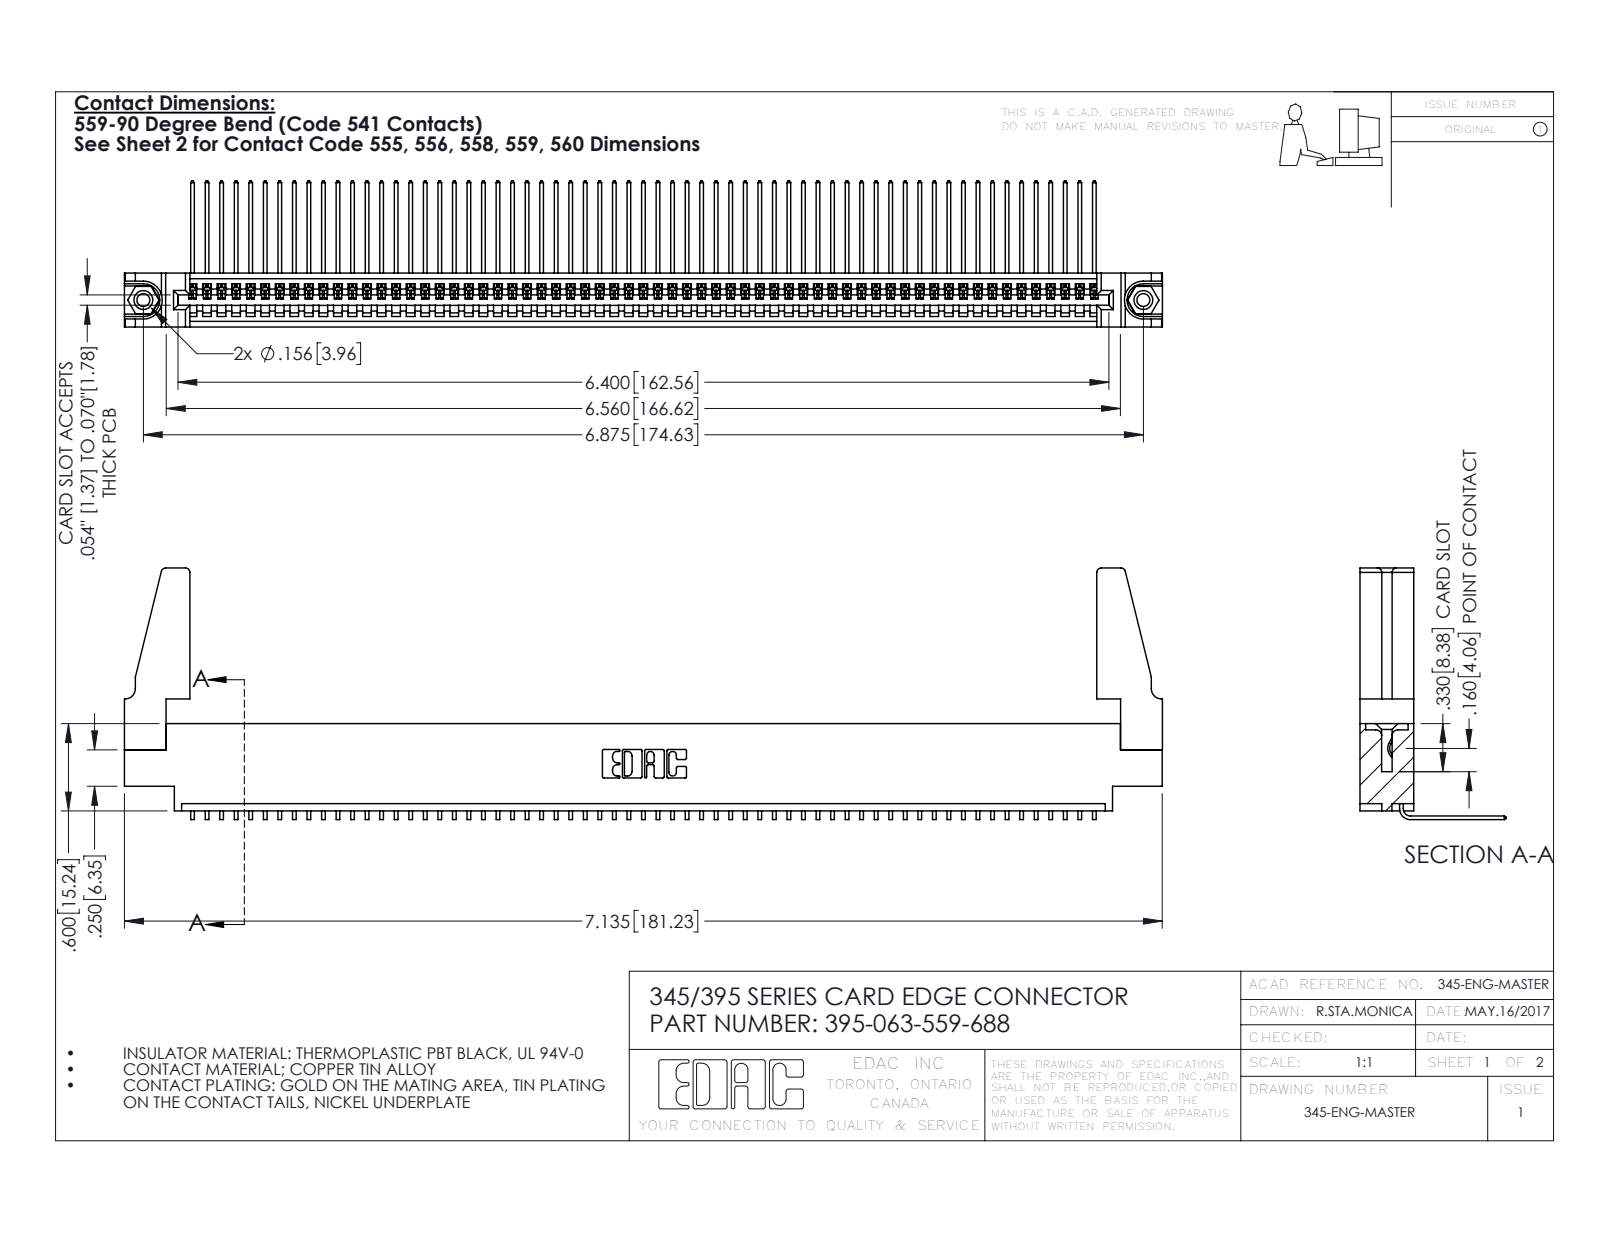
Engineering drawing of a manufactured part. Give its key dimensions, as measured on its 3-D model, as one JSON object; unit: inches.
{"part_name": "345-220-078_345-220-088; 345 Part_0.170 Offset - 0.156 Dia-TH; 345-250-001_345-250-001-102; 345-292-001_558 559 Tail - 1 (+1 more)", "step_written_by": "SolidWorks 2016 (CONFIG_CONTROL_DESIGN)", "units": "inches", "bodies": {"solids": 68, "faces": 4034, "planar": 2802, "cylindrical": 1216, "other": 16}, "overall_size": [7.136, 1.729, 1.005], "volume_in3": 1.265, "surface_area_in2": 43.42, "round_holes": [[0.089, 2], [0.125, 2], [0.156, 2], [0.064, 1]], "round_bosses_or_shafts": [[0.155, 2]], "partial_cylinders_radius": [[0.006, 126], [0.01, 22], [0.03, 8], [0.007, 6], [0.031, 6], [0.026, 3], [0.031, 2], [0.04, 2]], "face_to_face_distances": [0.072, 0.298, 0.37, 0.2, 0.098, 0.272, 0.025, 0.225, 0.175, 0.149], "hole_center_spacings": [0.27, 6.639, 6.875]}
